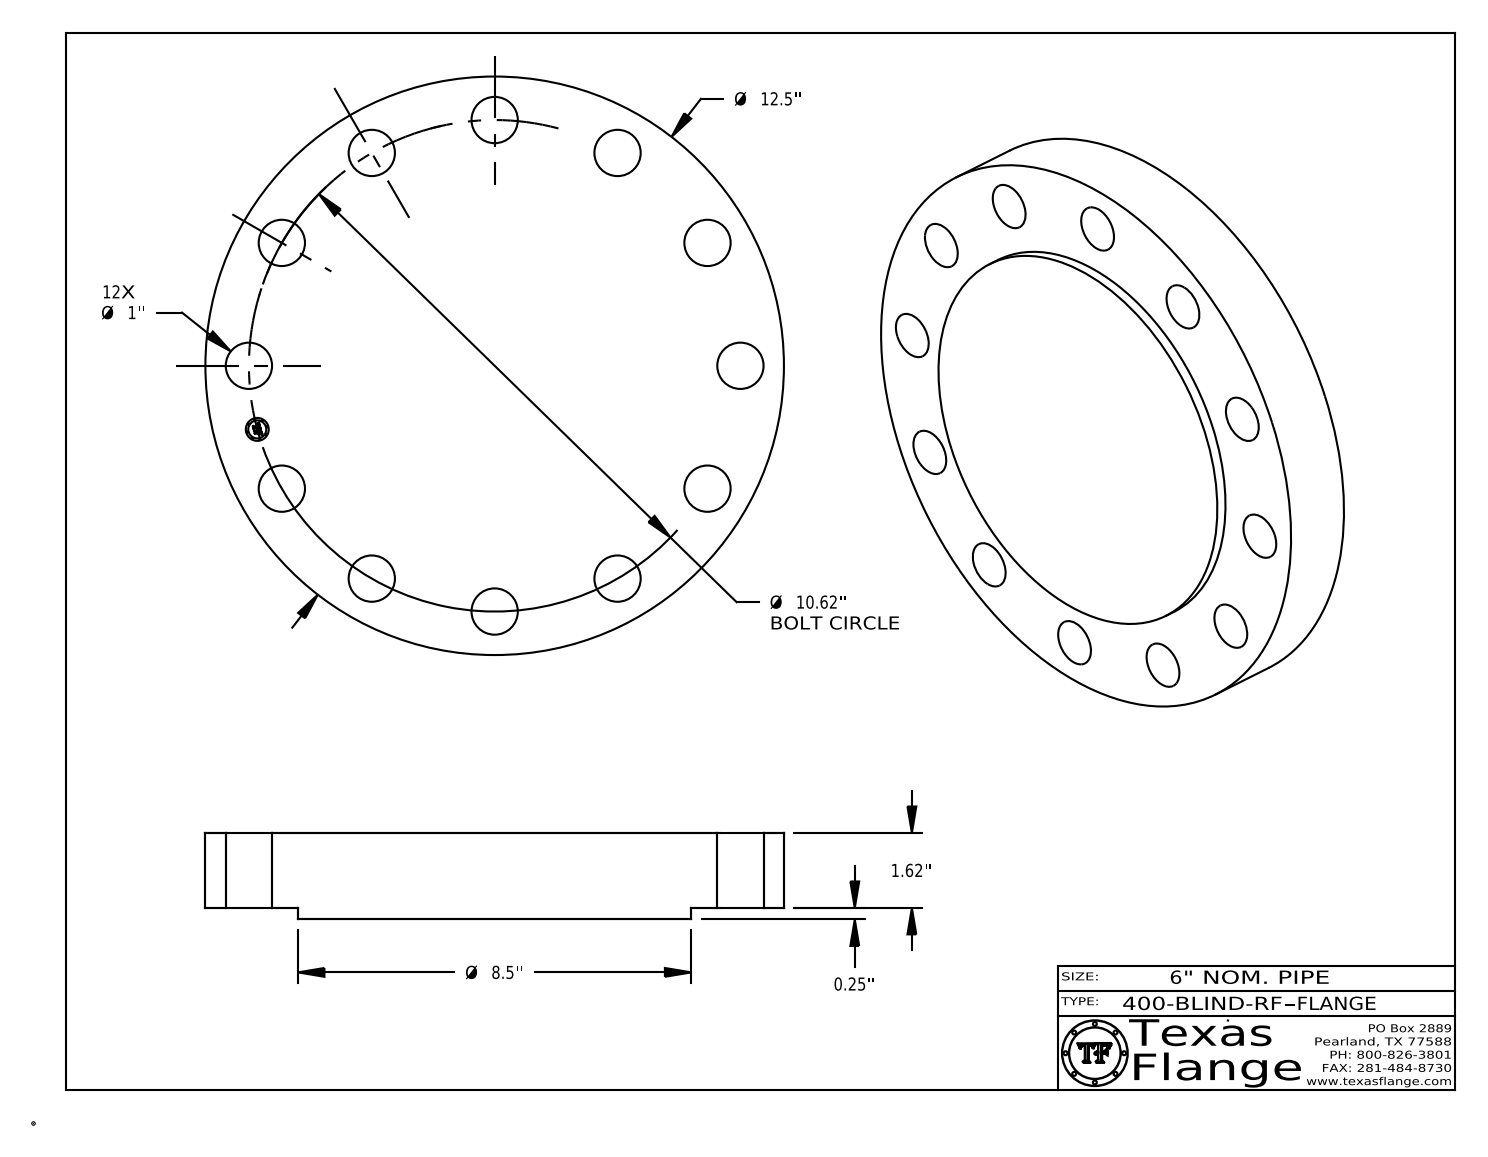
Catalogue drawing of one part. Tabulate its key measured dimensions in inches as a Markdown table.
| quantity | value |
| --- | --- |
| part name | 400-BLIND-RF |
| STEP written by | CATIA V5 STEP AP214 (AUTOMOTIVE_DESIGN) |
| units | inches |
| bodies | 1 solid, 416 faces (368 planar, 48 cylindrical, 0 other) |
| overall size | 12.5 × 12.5 × 1.87 |
| volume | 197.7 in³ |
| surface area | 358 in² |
| round holes (diameter × count) | 1 × 12, 0.495 × 1 |
| round bosses / shafts (diameter × count) | 0.03 × 8, 12.5 × 1, 8.5 × 1, 0.39 × 1 |
| main face-to-face distances | 1.87, 0.25, 1.62, 1.855, 1.605, 0.015, 0.148, 0.145, 0.027, 0.096 |
| hole center spacings | 10.258, 2.749, 5.31, 7.509, 9.197, 10.62, 2.748, 5.31 |
